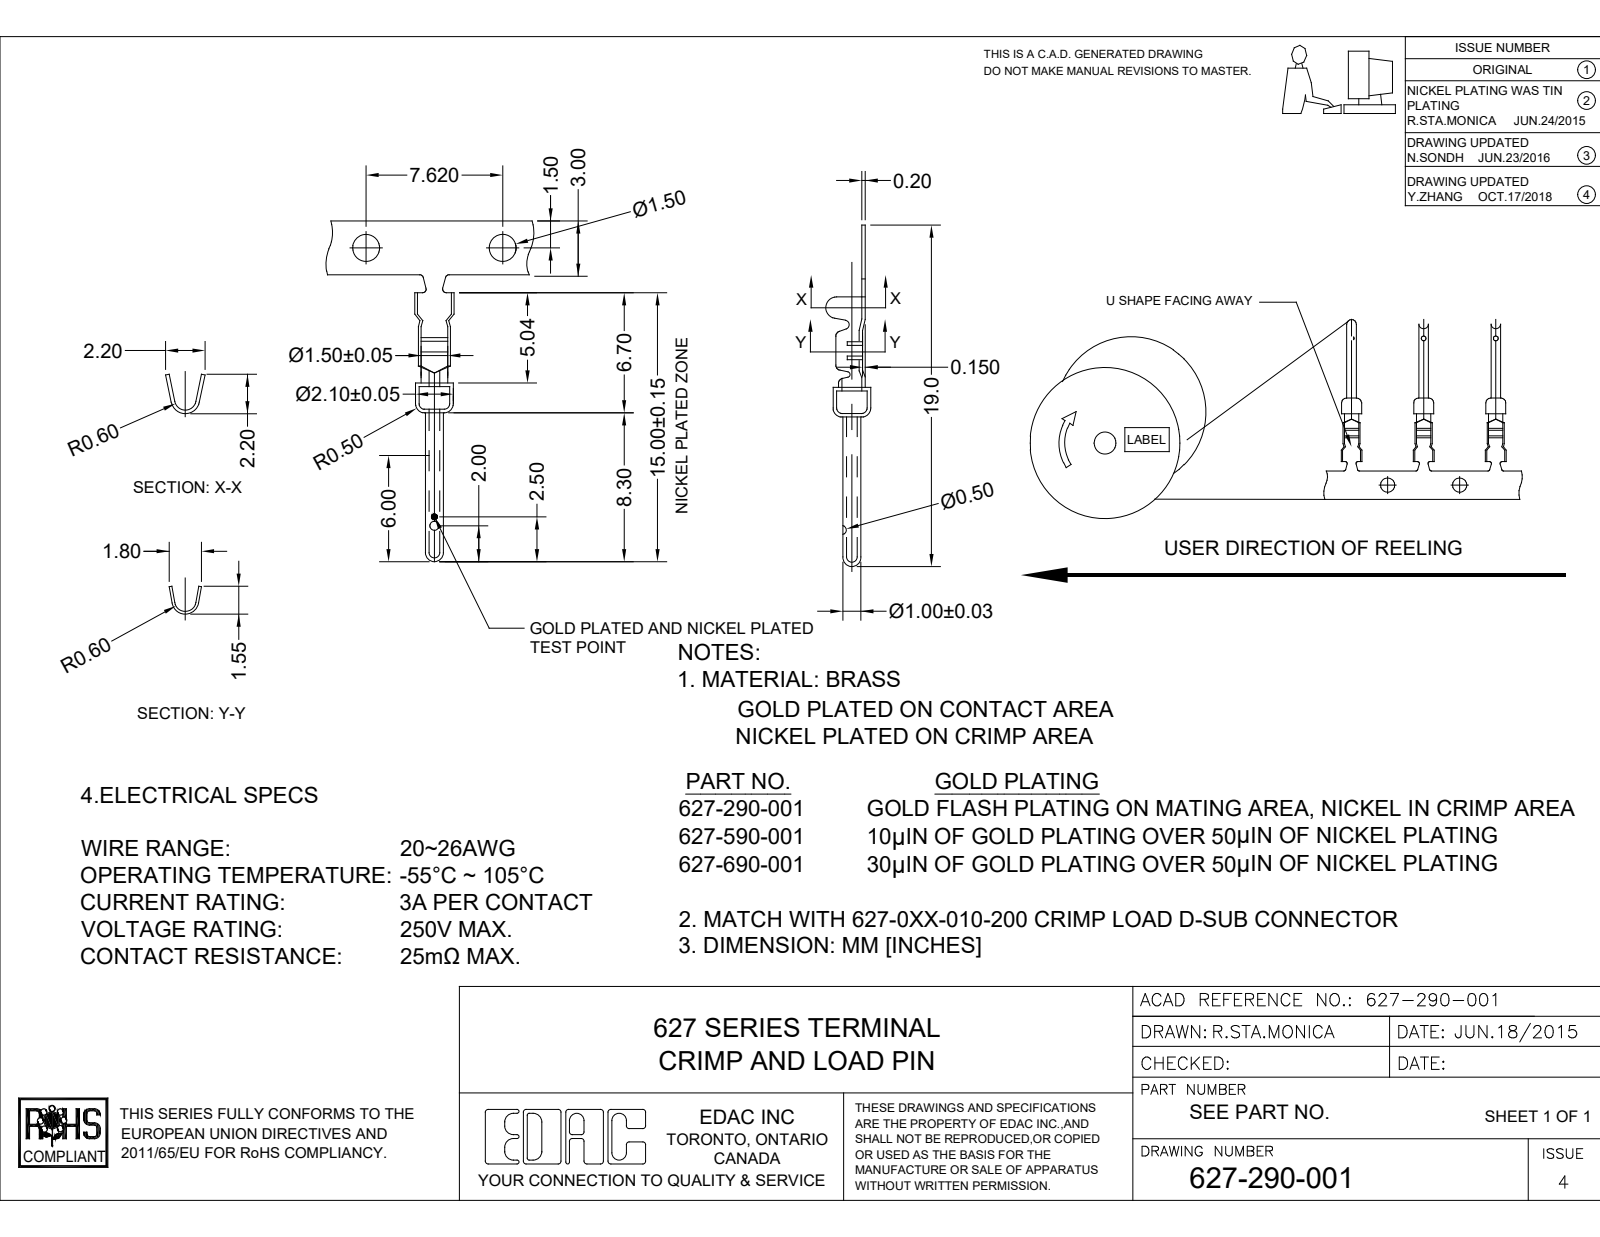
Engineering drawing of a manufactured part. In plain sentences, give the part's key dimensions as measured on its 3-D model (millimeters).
The part is named "627-290-001". Its 3-D file was written by "SolidWorks 2020 (AUTOMOTIVE_DESIGN)". It is 1 solid with 189 faces: 76 planar, 75 cylindrical and 38 other. Overall it measures 14.54 by 2.6 by 2.2 millimeters. Its volume is 8 cubic millimeters and its surface area 108 square millimeters. Round holes: 1 of diameter 0.2, 1 of diameter 0.5, 1 of diameter 0.7, 1 of diameter 1.8. Round bosses or shafts: 1 of diameter 2.1, 1 of diameter 1. Partial cylindrical surfaces (rounded edges, fillets, slot ends): 6 of radius 0.15, 6 of radius 0.6, 4 of radius 0.25, 4 of radius 0.3, 2 of radius 0.18, 2 of radius 0.2, 2 of radius 0.45, 1 of radius 0.41. The main face-to-face distances are 6.57, 6.72, 1.05, 2.6, 2.4, 1.57, 3.65, 2.92, 3.07, 3.97. The hole center spacings are 1.09.
